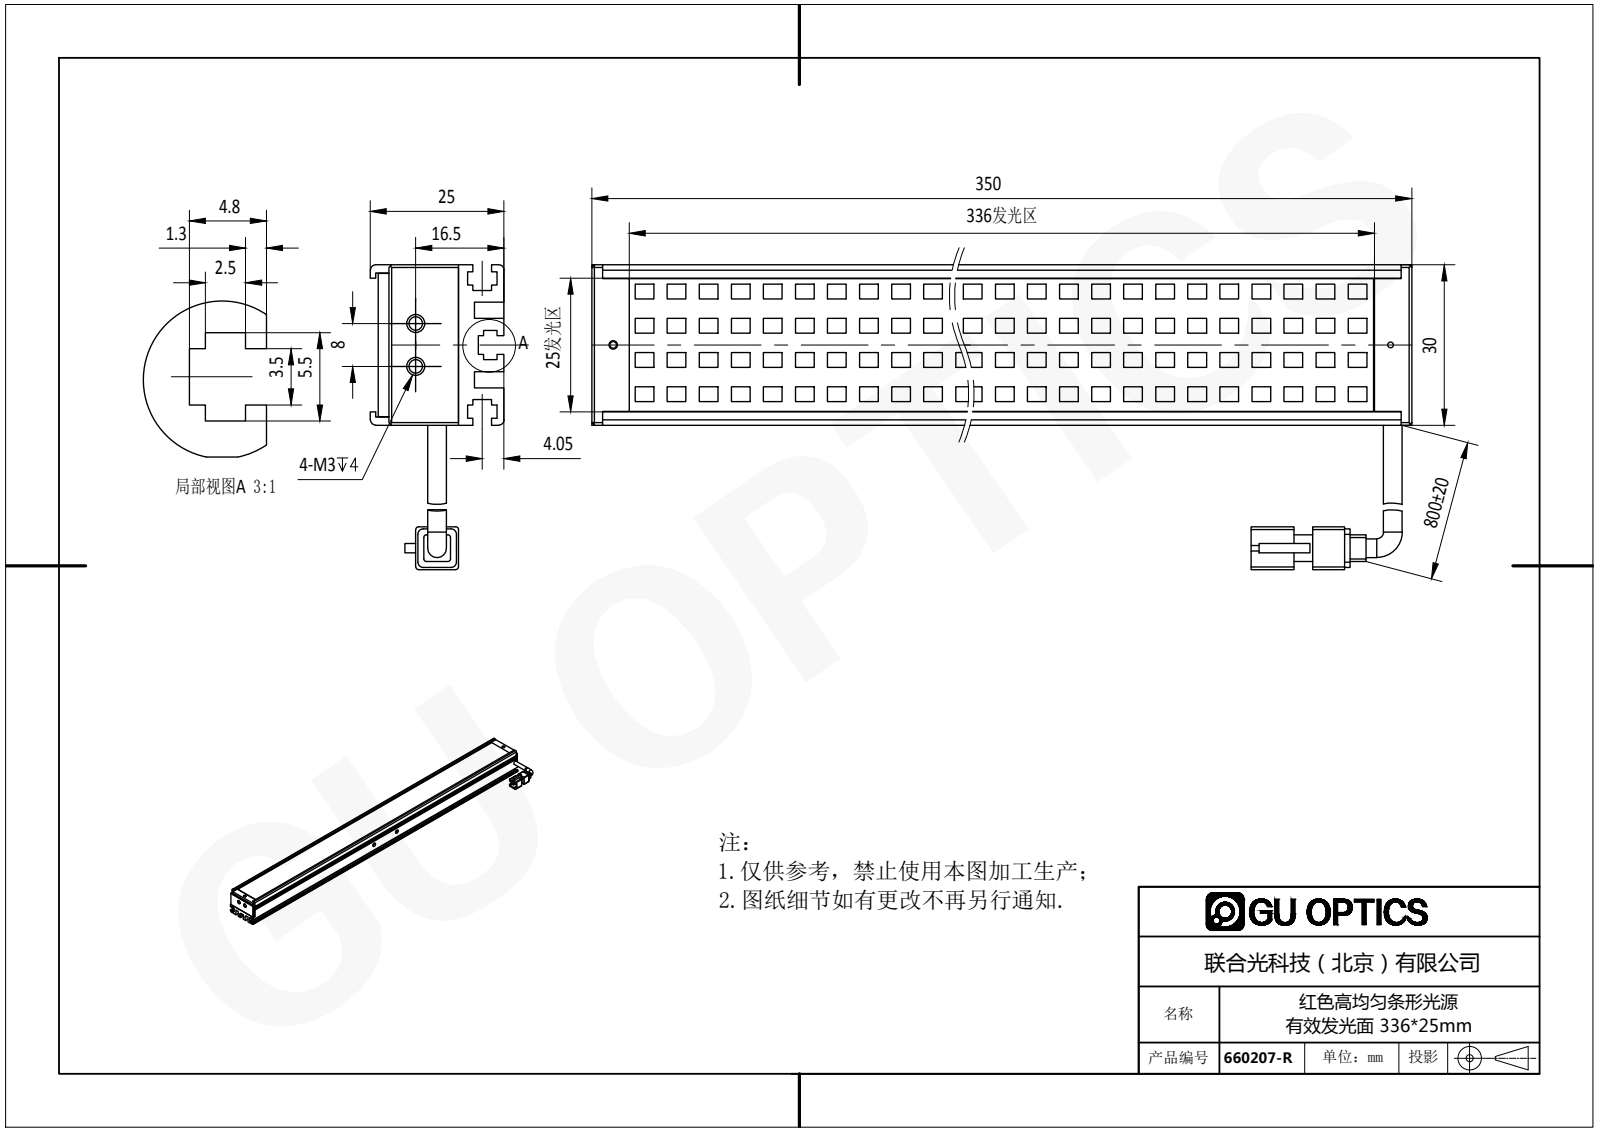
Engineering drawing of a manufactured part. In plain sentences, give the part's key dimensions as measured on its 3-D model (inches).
The part is named "660207-R". Its 3-D file was written by "SolidWorks 2016 (AUTOMOTIVE_DESIGN)". It is 6 solids with 1564 faces: 1378 planar, 83 cylindrical and 103 other. Overall it measures 13.78 by 2.244 by 0.984 inches. Its volume is 7.203 cubic inches and its surface area 186.8 square inches. Round holes: 5 of diameter 0.063, 2 of diameter 0.059, 2 of diameter 0.067, 2 of diameter 0.098, 2 of diameter 0.11, 2 of diameter 0.118, 1 of diameter 0.043, 1 of diameter 0.049, 1 of diameter 0.079. Round bosses or shafts: 2 of diameter 0.138. Partial cylindrical surfaces (rounded edges, fillets, slot ends): 12 of radius 0.039, 8 of radius 0.02, 1 of radius 0.065. The main face-to-face distances are 0.039, 0.512, 0.079, 0.098, 0.118, 1.083, 0.374, 0.177, 0.472, 0.594. The hole center spacings are 13.465, 0.276, 6.142, 6.147, 7.323, 7.328, 13.467, 0.315.
